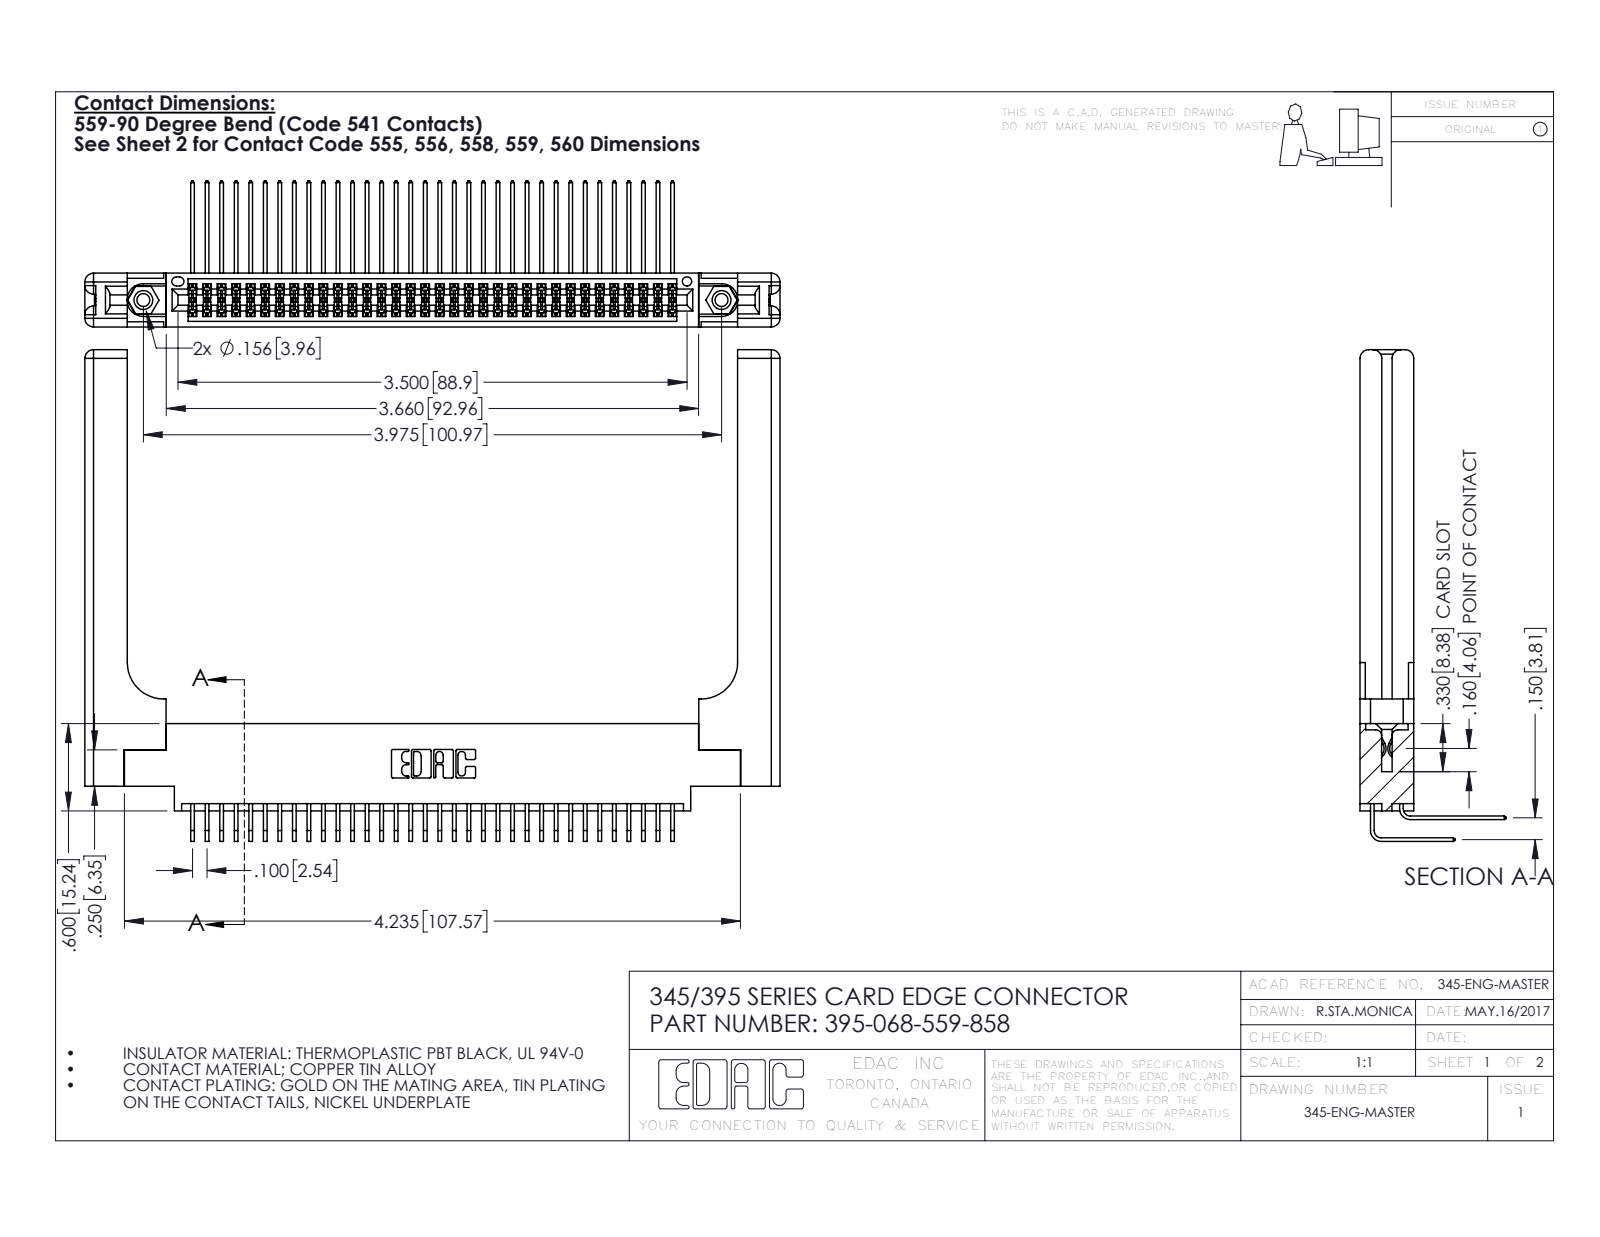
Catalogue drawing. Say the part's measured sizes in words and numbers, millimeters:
The part is named "395-068-559-858; 345-292-001_559 Tail - 2; 345-250-001_345-250-001-102; 345-220-058_345-220-058 (+2 more)". Its 3-D file was written by "SolidWorks 2016 (CONFIG_CONTROL_DESIGN)". It is 73 solids with 3922 faces: 2612 planar, 1250 cylindrical and 60 other. Overall it measures 121.4 by 85.8 by 25.5 millimeters. Its volume is 20 470 cubic millimeters and its surface area 24 630 square millimeters. Round holes: 2 of diameter 2.3, 2 of diameter 3.2, 2 of diameter 4, 1 of diameter 1.6. Round bosses or shafts: 2 of diameter 3.9. Partial cylindrical surfaces (rounded edges, fillets, slot ends): 103 of radius 0.2, 22 of radius 0.3, 16 of radius 1.5, 6 of radius 0.2, 6 of radius 0.8, 3 of radius 0.7, 2 of radius 0.4, 2 of radius 0.5. The main face-to-face distances are 9.4, 1.8, 7.6, 2.5, 6.9, 0.6, 5.1, 5.7, 3.8, 4.4. The hole center spacings are 6.9, 95, 101.
